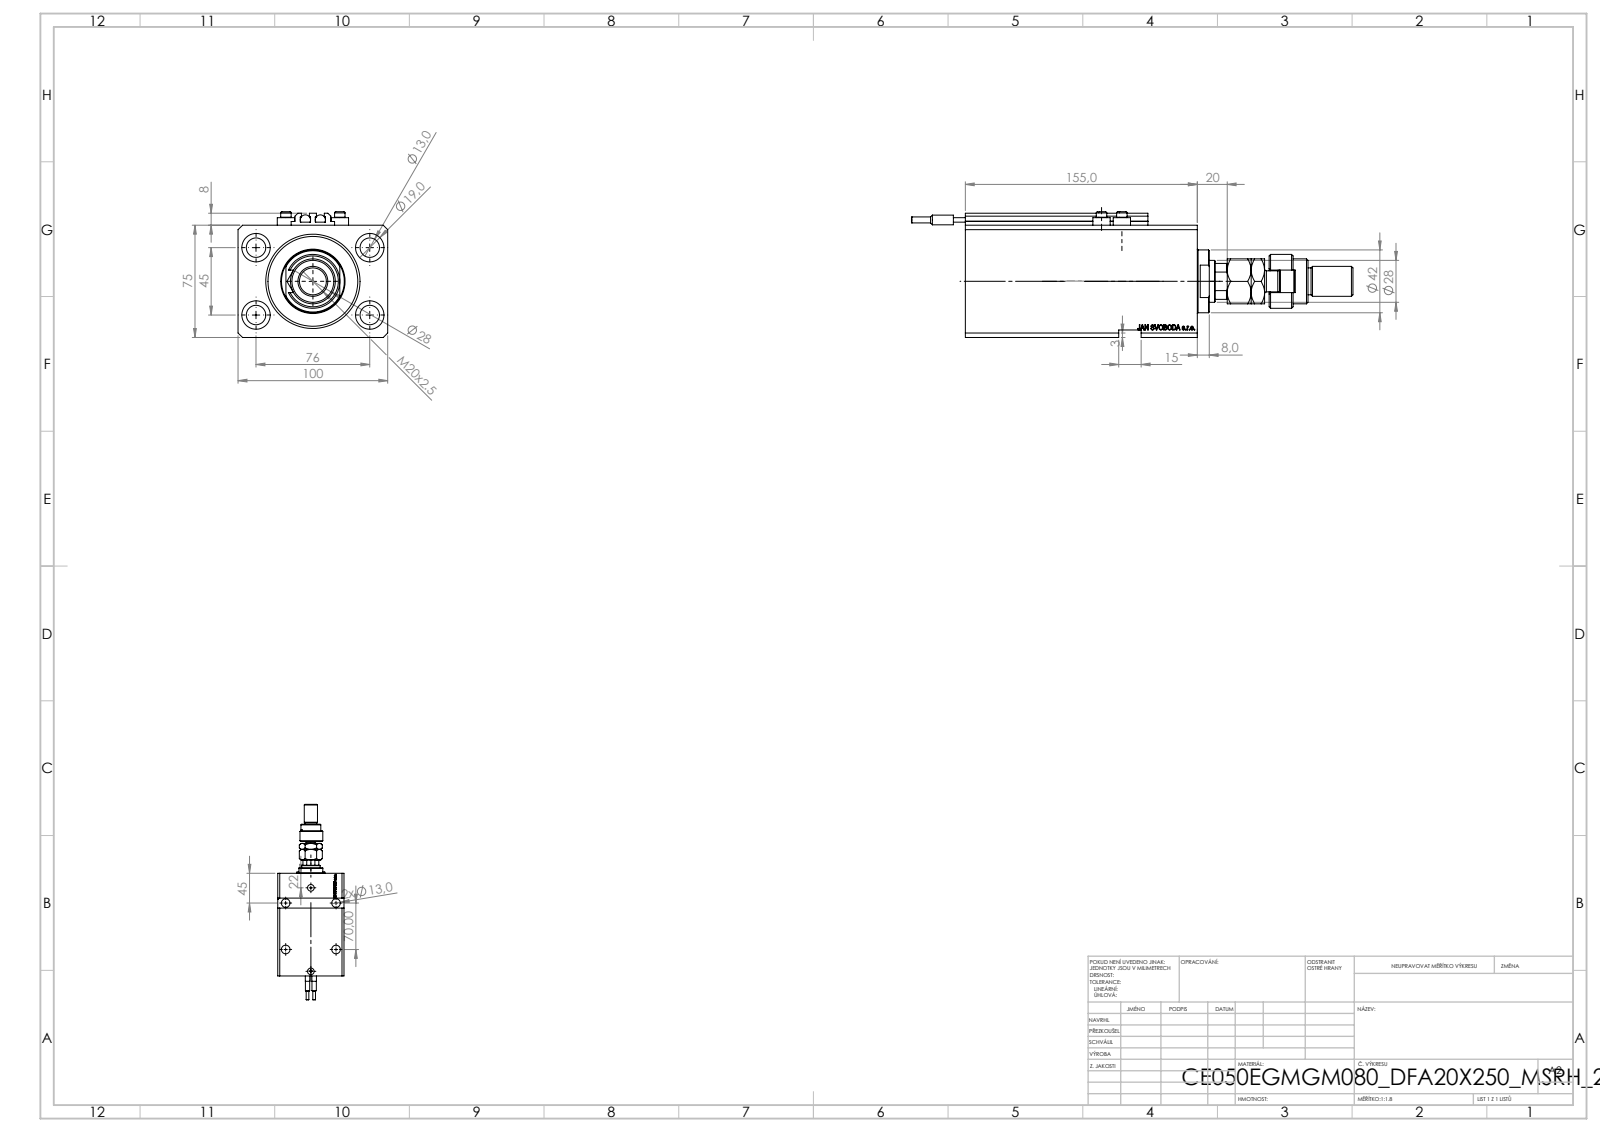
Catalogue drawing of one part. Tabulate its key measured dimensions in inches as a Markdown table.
| quantity | value |
| --- | --- |
| part name | SWITCH_V250CE; V250CE_VC_E; ALLEN BOLT V250CE; V250CE_E_Body (+3 more) |
| STEP written by | SolidWorks 2019 (CONFIG_CONTROL_DESIGN) |
| units | inches |
| bodies | 12 solids, 1245 faces (595 planar, 171 cylindrical, 479 other) |
| overall size | 11.614 × 3.937 × 3.307 |
| volume | 60.61 in³ |
| surface area | 297.5 in² |
| round holes (diameter × count) | 0.512 × 8, 0.049 × 4, 0.157 × 4, 0.748 × 4, 0.394 × 2, 0.518 × 2, 0.787 × 2, 0.728 × 1, 1.102 × 1, 1.969 × 1, 2.48 × 1 |
| round bosses / shafts (diameter × count) | 0.457 × 4, 0.276 × 4, 0.268 × 2, 0.256 × 2, 0.157 × 2, 1.654 × 1, 1.417 × 1, 1.181 × 1 |
| partial cylindrical surfaces (radius × count) | 0.008 × 10, 0.295 × 1, 0.472 × 1, 0.531 × 1 |
| main face-to-face distances | 2.953, 3.937, 0.787, 6.102, 0.469, 5.634, 5.315, 4.846, 0.394, 0.118 |
| hole center spacings | 1.739, 2.992, 0.535, 0.816, 1.086, 1.324, 1.417, 1.515 |
